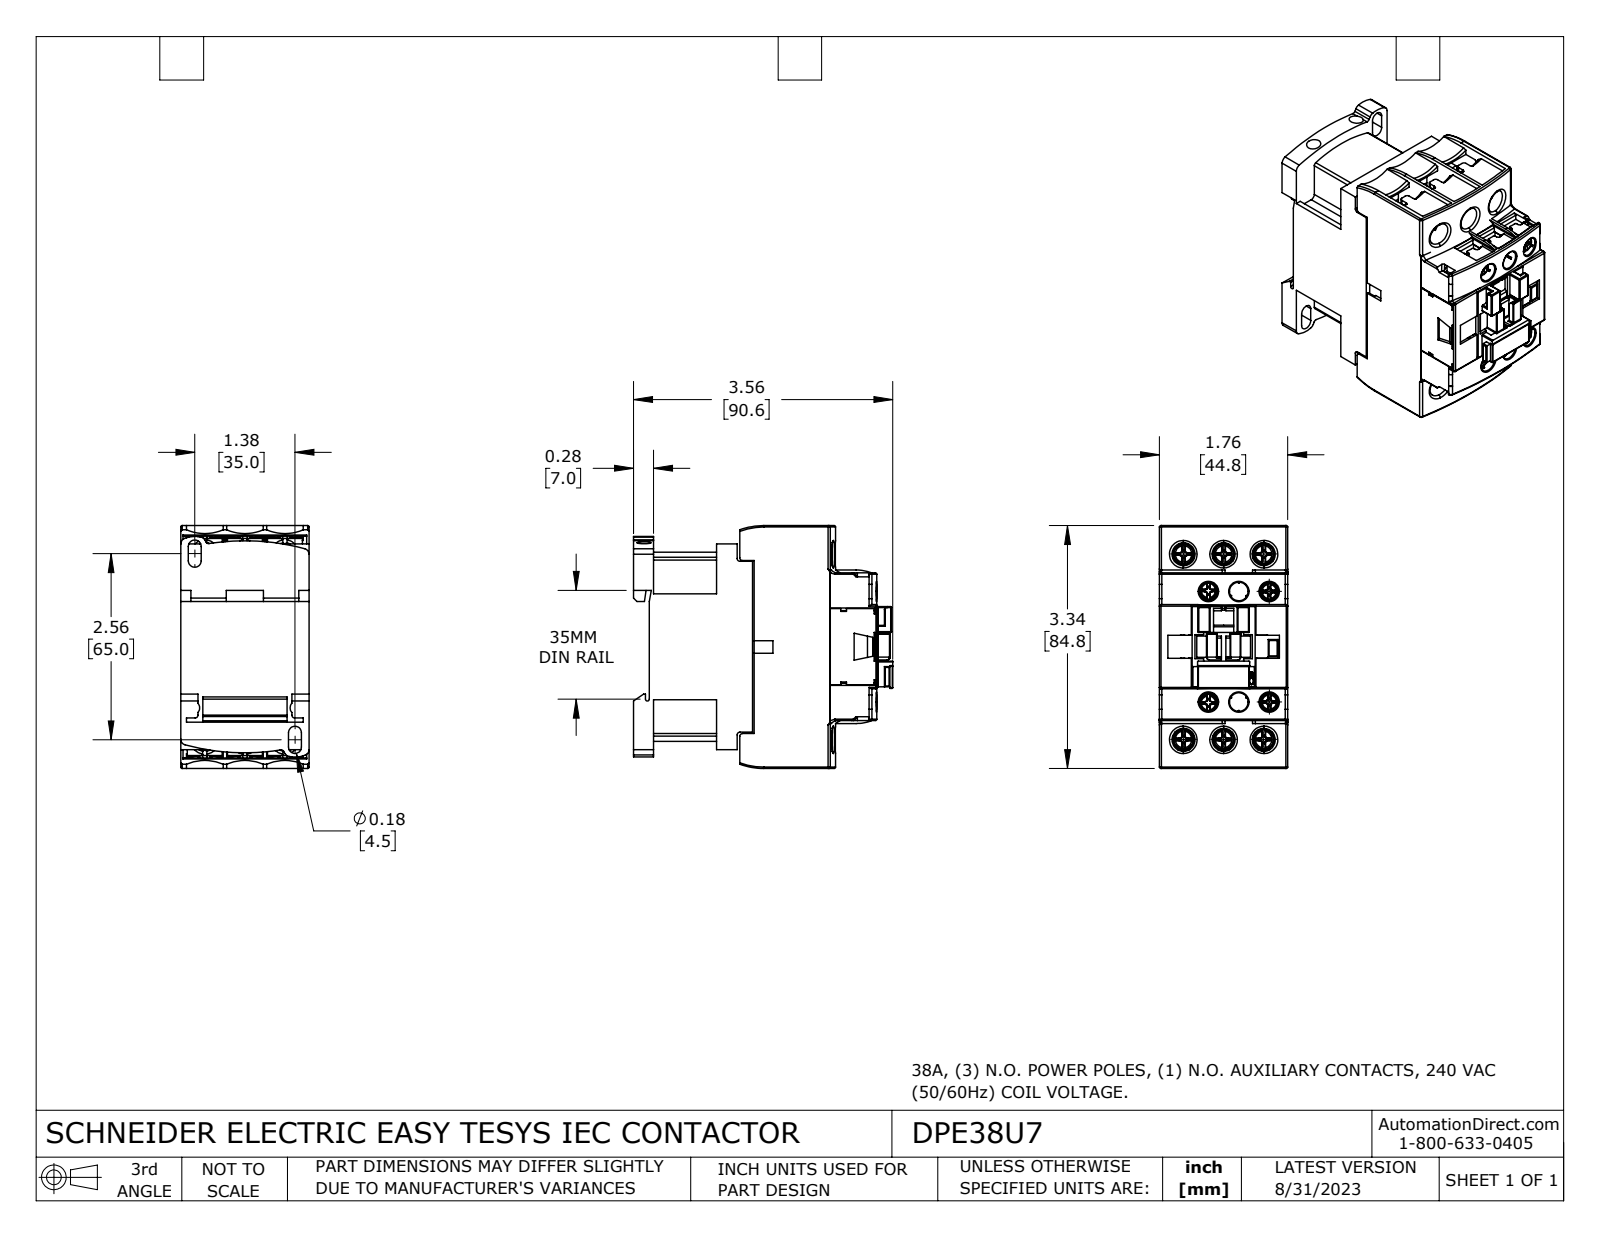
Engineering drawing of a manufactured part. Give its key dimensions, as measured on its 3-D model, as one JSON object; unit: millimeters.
{"part_name": "DPE38U7", "step_written_by": "SolidWorks 2021 (CONFIG_CONTROL_DESIGN)", "units": "millimeters", "bodies": {"solids": 16, "faces": 2674, "planar": 1724, "cylindrical": 584, "other": 366}, "overall_size": [90.6, 84.8, 44.8], "volume_mm3": 205800, "surface_area_mm2": 64770, "round_holes": [[6.5, 6], [8, 6], [5, 2]], "round_bosses_or_shafts": [[4, 8], [3.2, 6], [3.5, 4], [3.4, 4], [2.7, 4], [10, 3]], "partial_cylinders_radius": [[0.3, 58], [0.2, 36], [1, 36], [0.5, 34], [16, 18], [0.2, 17], [2, 9], [0.8, 8]], "face_to_face_distances": [44.8, 14, 0.6, 1.5, 27.7, 27.1, 1.2, 0.8, 35.1, 36], "hole_center_spacings": [10.6, 14, 40, 66.3, 38.6, 64.8, 14, 14.2]}
